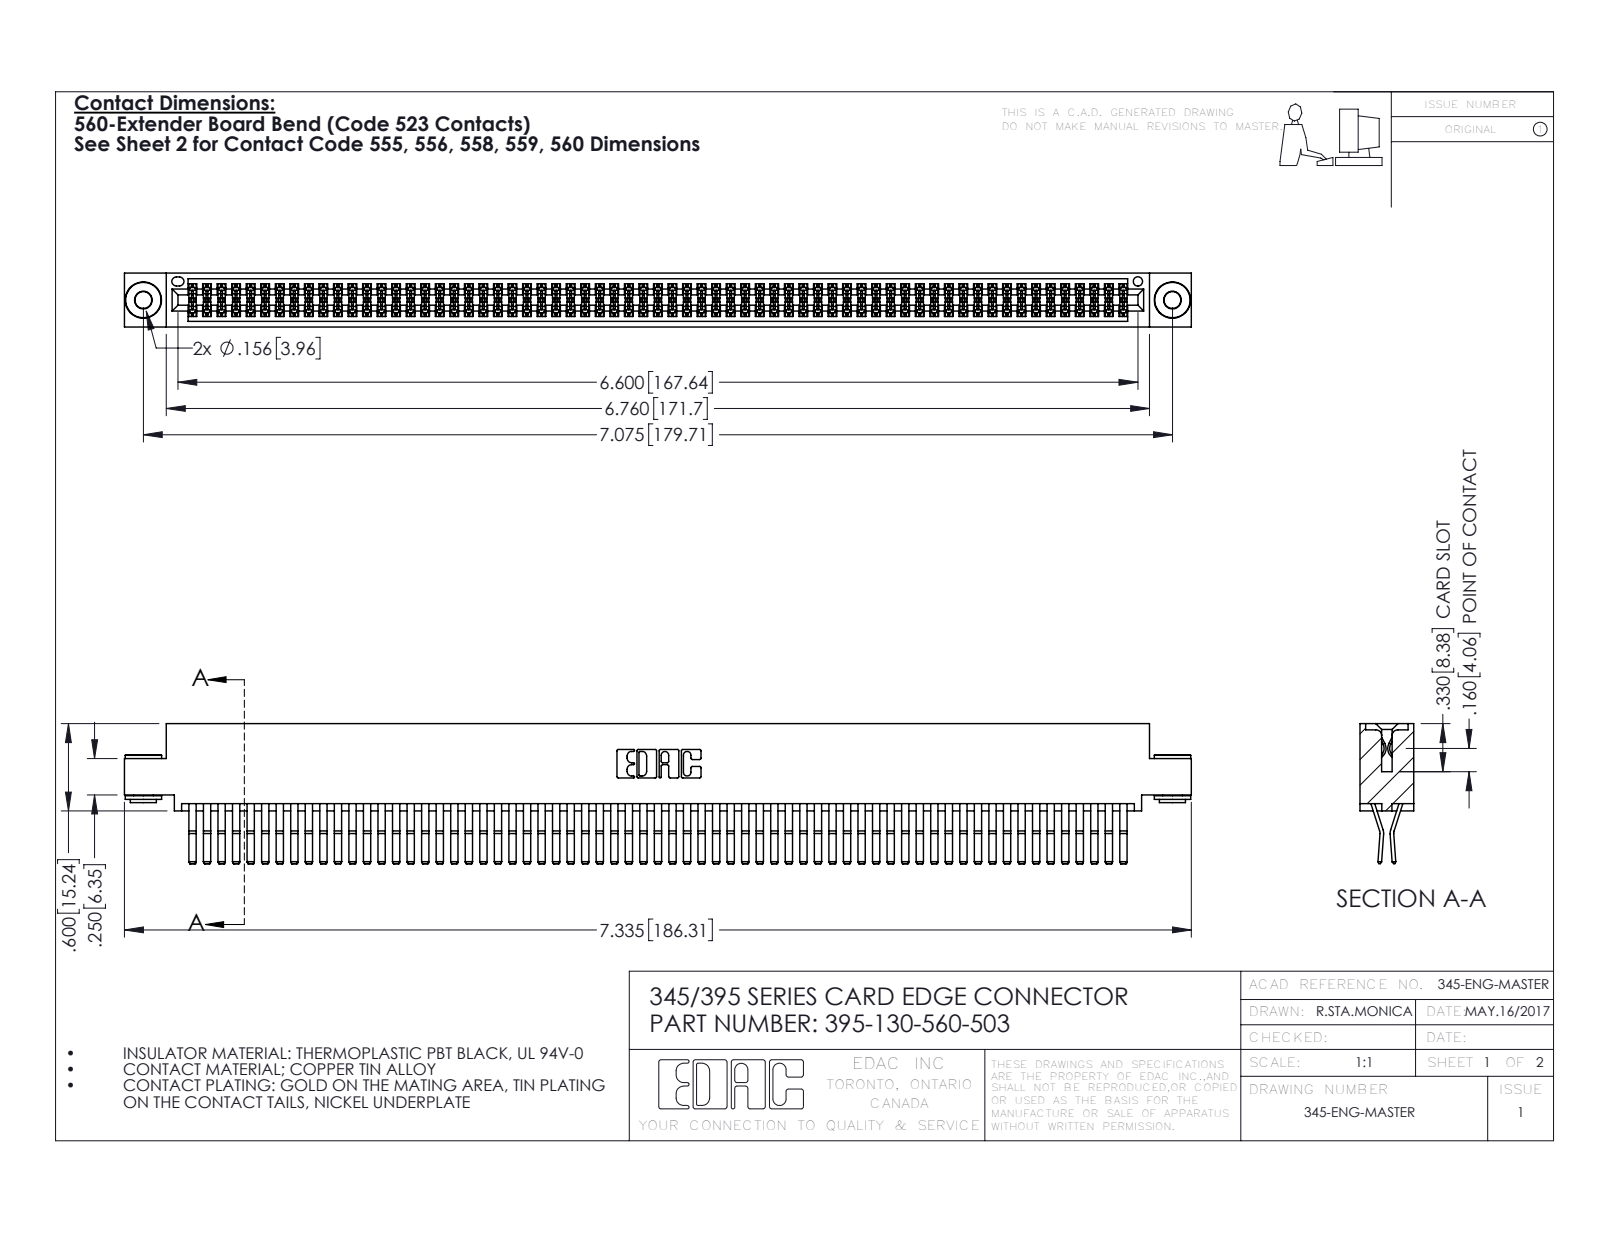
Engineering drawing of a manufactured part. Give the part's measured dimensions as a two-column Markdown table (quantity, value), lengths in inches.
| quantity | value |
| --- | --- |
| part name | 345-292-001_560 Tail; 345-250-002_345-250-002-102; 345 Part_0.110 Offset - 0.156 Dia-TH; 395-130-560-503 |
| STEP written by | SolidWorks 2016 (CONFIG_CONTROL_DESIGN) |
| units | inches |
| bodies | 133 solids, 6928 faces (4384 planar, 2536 cylindrical, 8 other) |
| overall size | 7.335 × 0.962 × 0.37 |
| volume | 1.166 in³ |
| surface area | 48.33 in² |
| round holes (diameter × count) | 0.116 × 2, 0.156 × 2, 0.064 × 1 |
| round bosses / shafts (diameter × count) | 0.25 × 2, 0.18 × 2, 0.136 × 2 |
| partial cylindrical surfaces (radius × count) | 0.006 × 196, 0.01 × 22, 0.007 × 6, 0.031 × 6, 0.026 × 3, 0.01 × 2, 0.014 × 2, 0.019 × 2 |
| main face-to-face distances | 0.025, 0.072, 0.298, 0.37, 0.2, 0.098, 0.272, 0.225, 0.175, 0.149 |
| hole center spacings | 0.27, 6.839, 7.075 |
